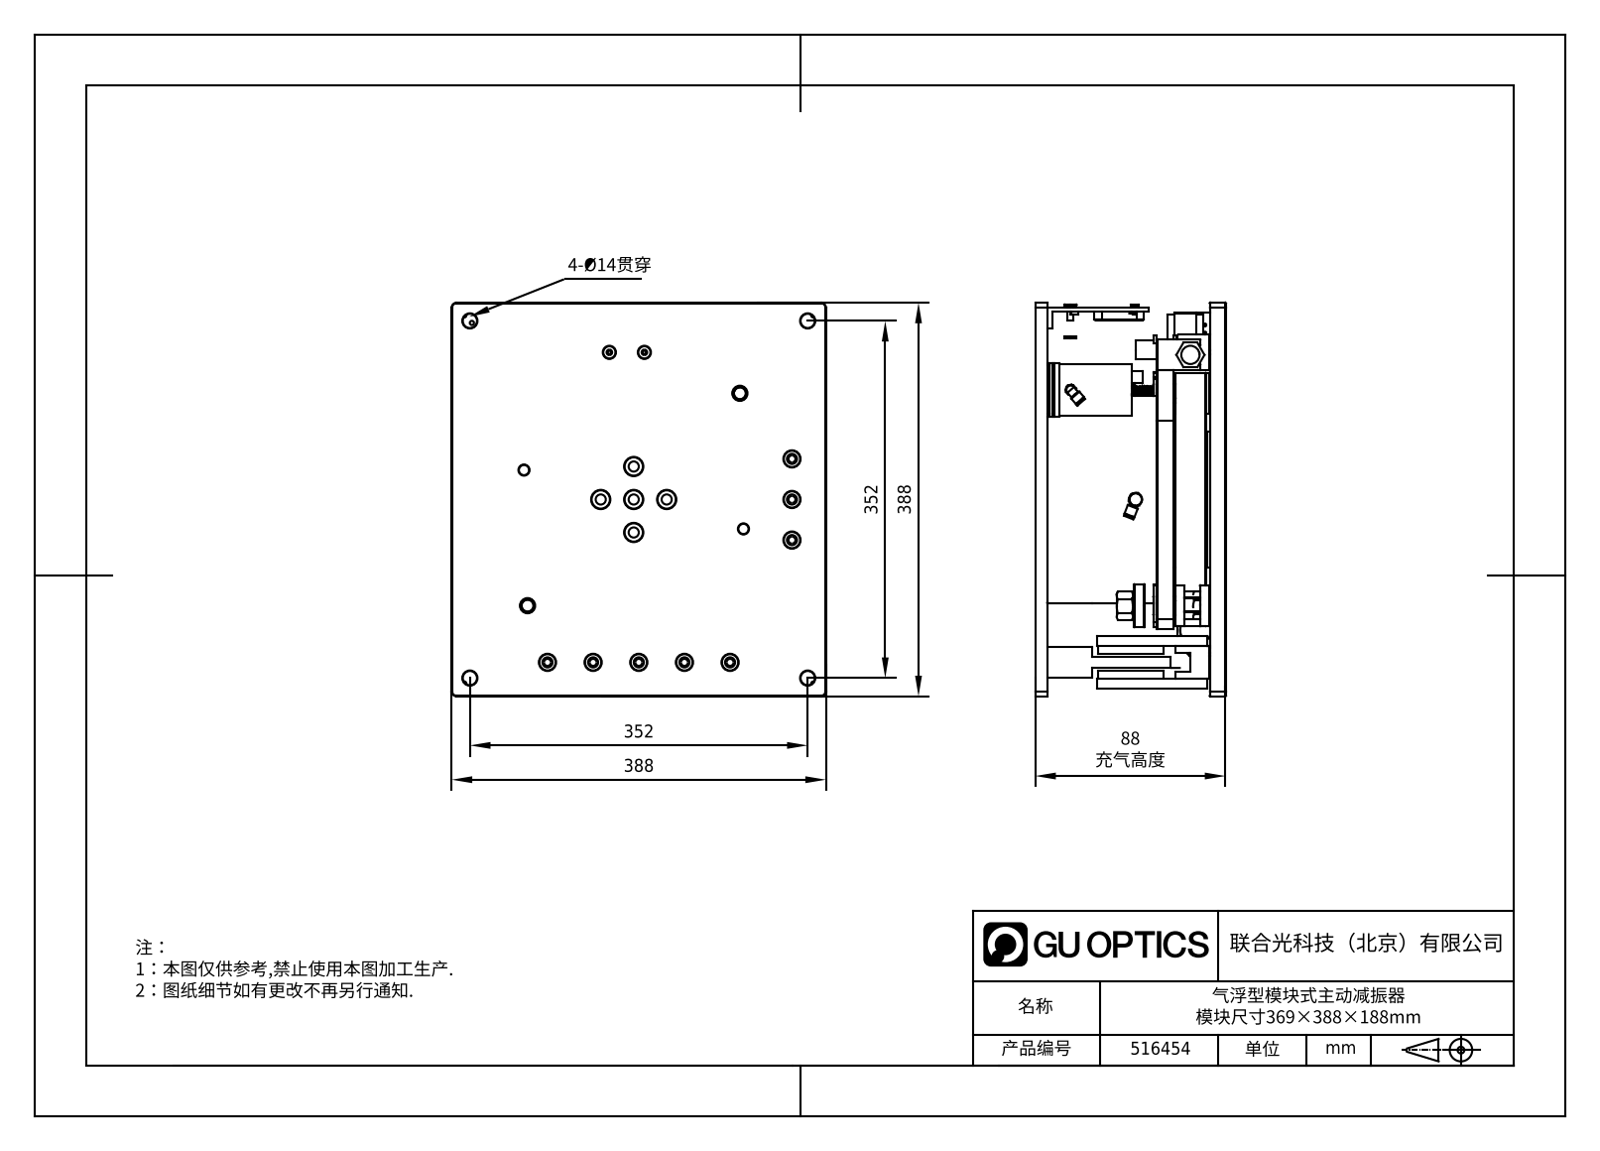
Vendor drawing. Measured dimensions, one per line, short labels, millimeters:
name: 516454
written by: SolidWorks 2020 (CONFIG_CONTROL_DESIGN)
unit: mm
bodies: 0 solids, 662 faces (346 planar, 221 cylindrical, 95 other)
size: 388 × 369 × 188
holes: 14× ⌀10, 8× ⌀16, 6× ⌀14, 6× ⌀18, 5× ⌀7, 4× ⌀12, 3× ⌀3.2, 2× ⌀2.5, 2× ⌀8.5, 2× ⌀40, 1× ⌀6, 1× ⌀8.25
bosses: 34× ⌀11, 8× ⌀5, 8× ⌀4.2, 7× ⌀18, 6× ⌀7, 5× ⌀1, 4× ⌀10, 4× ⌀8.4
rounds: 11× R2, 7× R5, 5× R0.5, 4× R2.5, 4× R10, 3× R1, 3× R3.4, 2× R4.9
face distances: 16, 12, 160, 172, 188, 176, 52, 20.5, 11, 34
hole spacings: 32.5, 45, 45.96, 127.11, 172.52, 25.46, 90, 125.04
